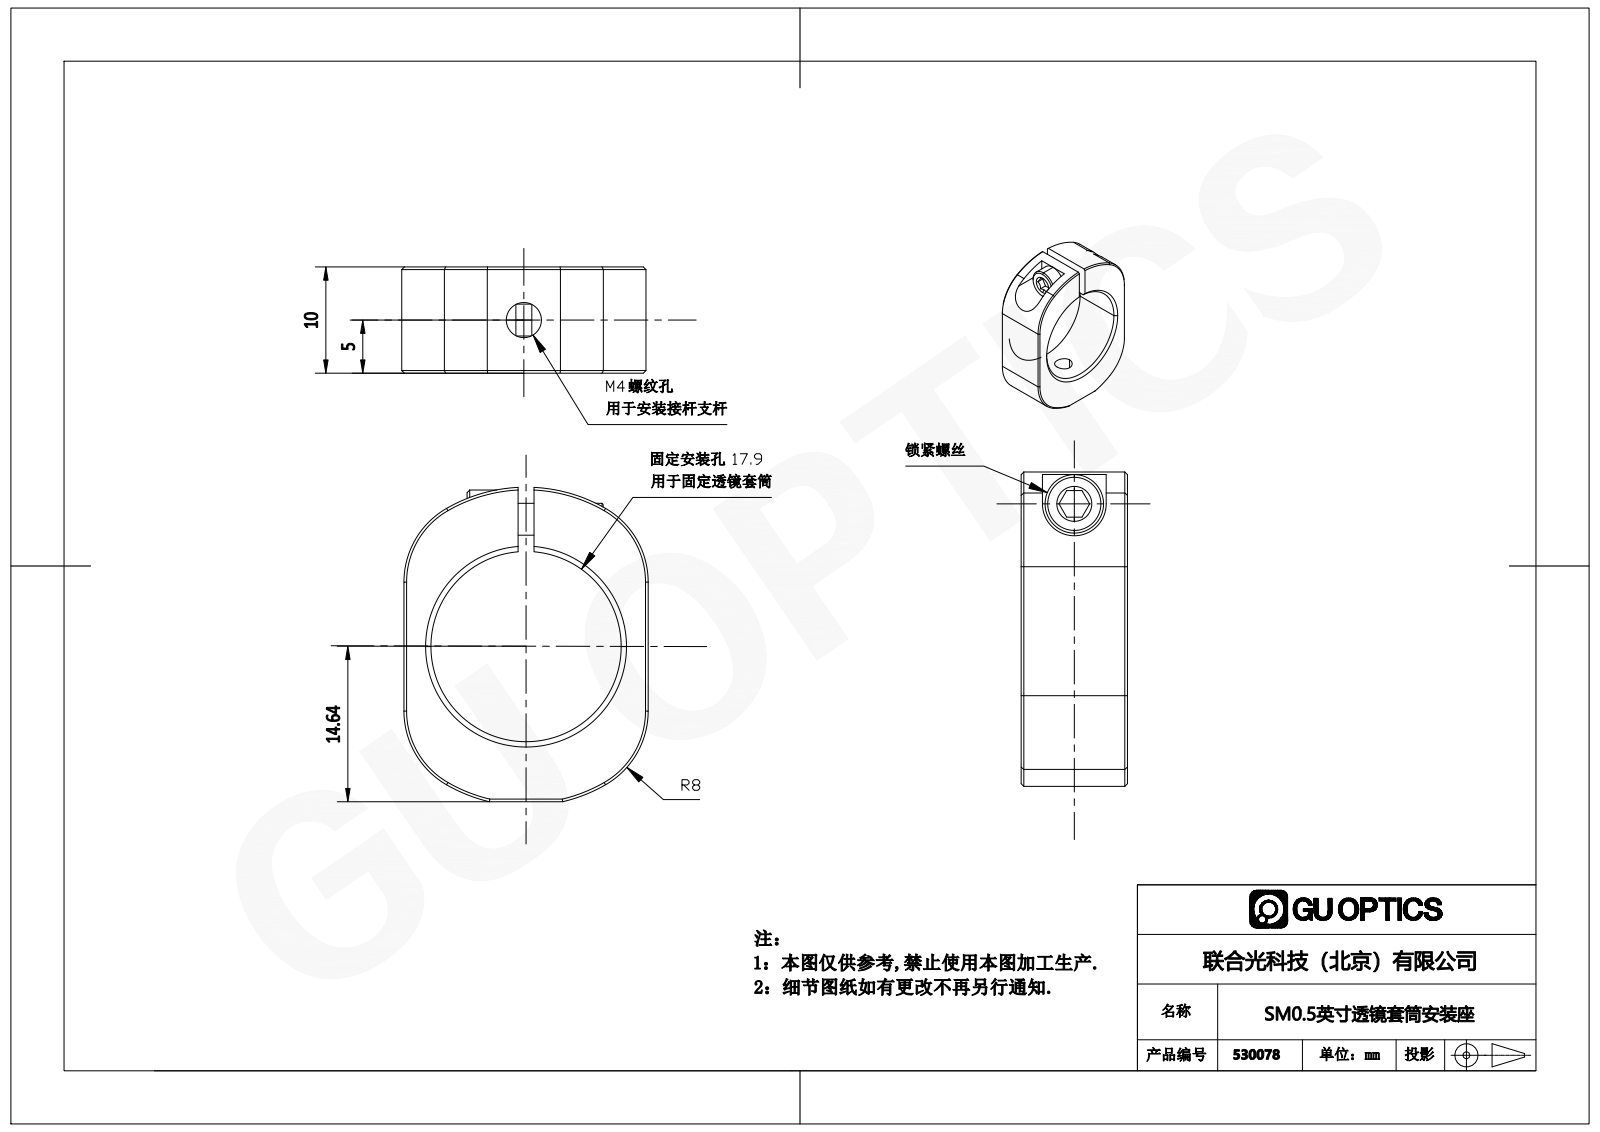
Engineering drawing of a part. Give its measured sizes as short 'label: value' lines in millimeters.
written by: SolidWorks 2018 (CONFIG_CONTROL_DESIGN)
unit: mm
bodies: 0 solids, 72 faces (24 planar, 20 cylindrical, 28 other)
size: 29.58 × 22.98 × 10
holes: 1× ⌀2.5, 1× ⌀3.3, 1× ⌀17.9
bosses: 1× ⌀5.5, 1× ⌀3
rounds: 4× R8, 1× R3, 1× R15
face distances: 10, 22.98, 10.74, 12.24, 1.5, 2, 8, 14.24, 3.5, 8.74
